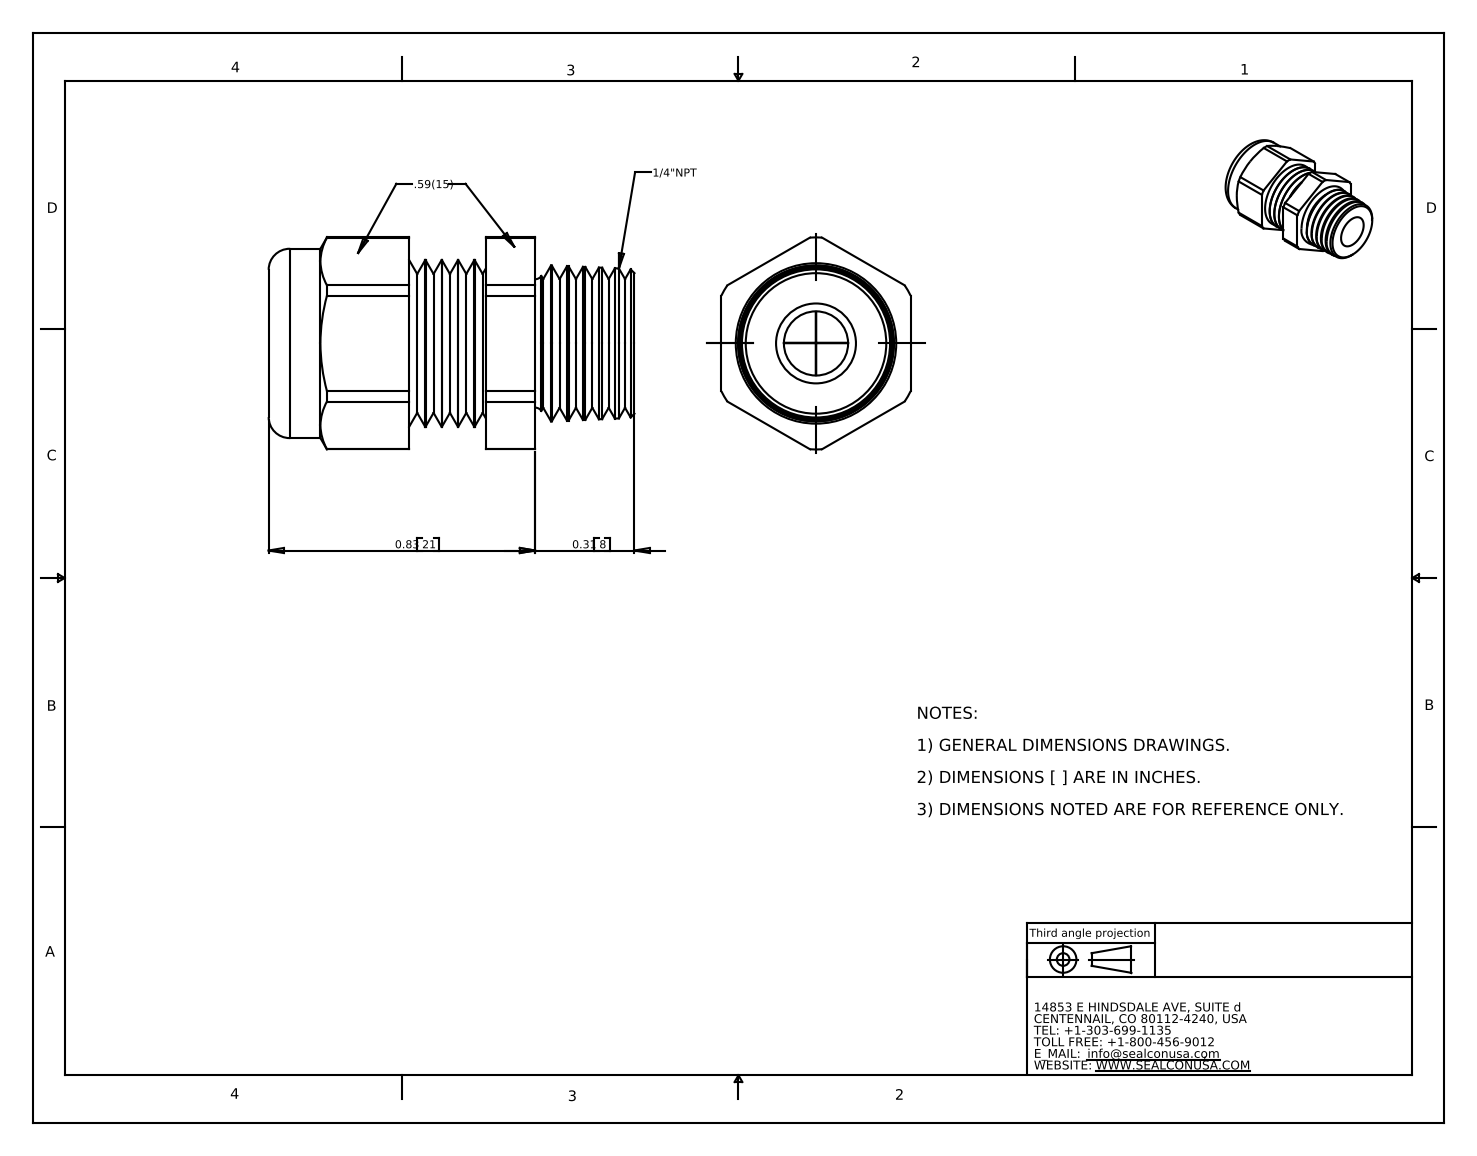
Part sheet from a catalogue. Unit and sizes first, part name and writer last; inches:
Units: inches
Overall size (bounding box): 1.14 × 0.661 × 0.59
Round holes (diameter × count): ⌀0.2 ×1, ⌀0.417 ×1
Round bosses / shafts (diameter × count): ⌀0.59 ×1, ⌀0.519 ×1
Partial cylindrical surfaces — rounded edges, fillets, slot ends (radius × count): R0.33 ×1
Main face-to-face distances: 0.59, 0.669, 0.979, 0.31, 0.141, 0.81, 1.12, 0.418, 0.277, 0.392
Volume: 0.216 in³ · Surface area: 4.771 in²
Bodies: 2 solids, 124 faces (20 planar, 32 cylindrical, 72 other)
Part name (STEP PRODUCT): CD07AR-GY
STEP written by: SolidWorks 2007 (CONFIG_CONTROL_DESIGN)
